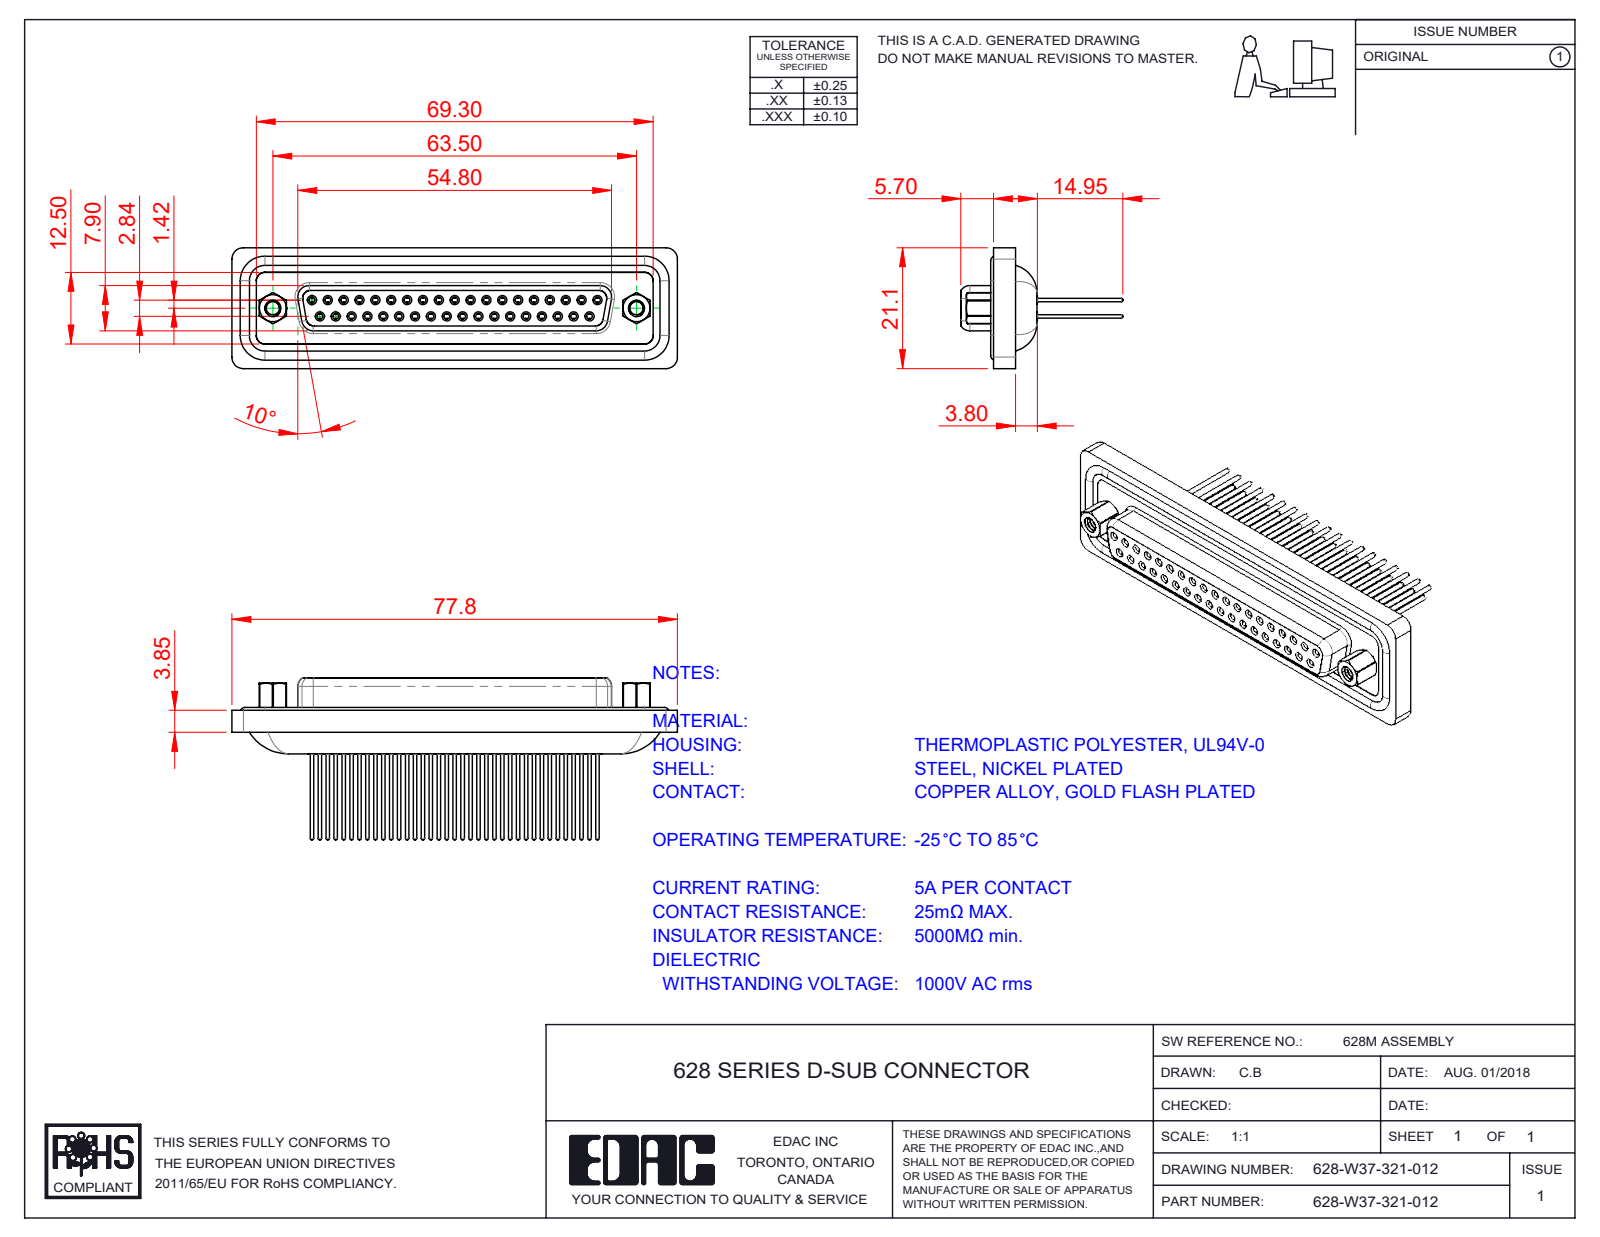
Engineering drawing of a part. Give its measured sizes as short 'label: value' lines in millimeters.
name: 628W Contact Row 2_21; 628W 4-40 Hex Standoff; 628W Waterproof Housing_37 Contacts; 628-W37-321-012 (+4 more)
written by: SolidWorks 2020 (CONFIG_CONTROL_DESIGN)
unit: mm
bodies: 45 solids, 2532 faces (656 planar, 997 cylindrical, 879 other)
size: 77.8 × 28.3 × 21.1
volume: 11 160 mm³; area: 18 575 mm²
holes: 37× ⌀1, 37× ⌀1.1, 37× ⌀1.5, 37× ⌀1.7, 37× ⌀1.8, 37× ⌀2, 2× ⌀2.26, 2× ⌀2.29, 2× ⌀4, 2× ⌀4.8, 2× ⌀5
bosses: 41× ⌀1.6, 37× ⌀2.2, 37× ⌀0.6, 8× ⌀1.5, 2× ⌀4.9, 2× ⌀2.79
rounds: 16× R2, 14× R1.5, 8× R1.35, 6× R2.7, 4× R0.5, 4× R0.9, 4× R1.6, 4× R1.75
face distances: 0.4, 7.45, 7.5, 8.45, 6.2, 13.65, 3.75, 4.1, 1.1, 2.75
hole spacings: 3.16, 2.77, 5.54, 8.31, 5.04, 7.49, 11.08, 13.85
